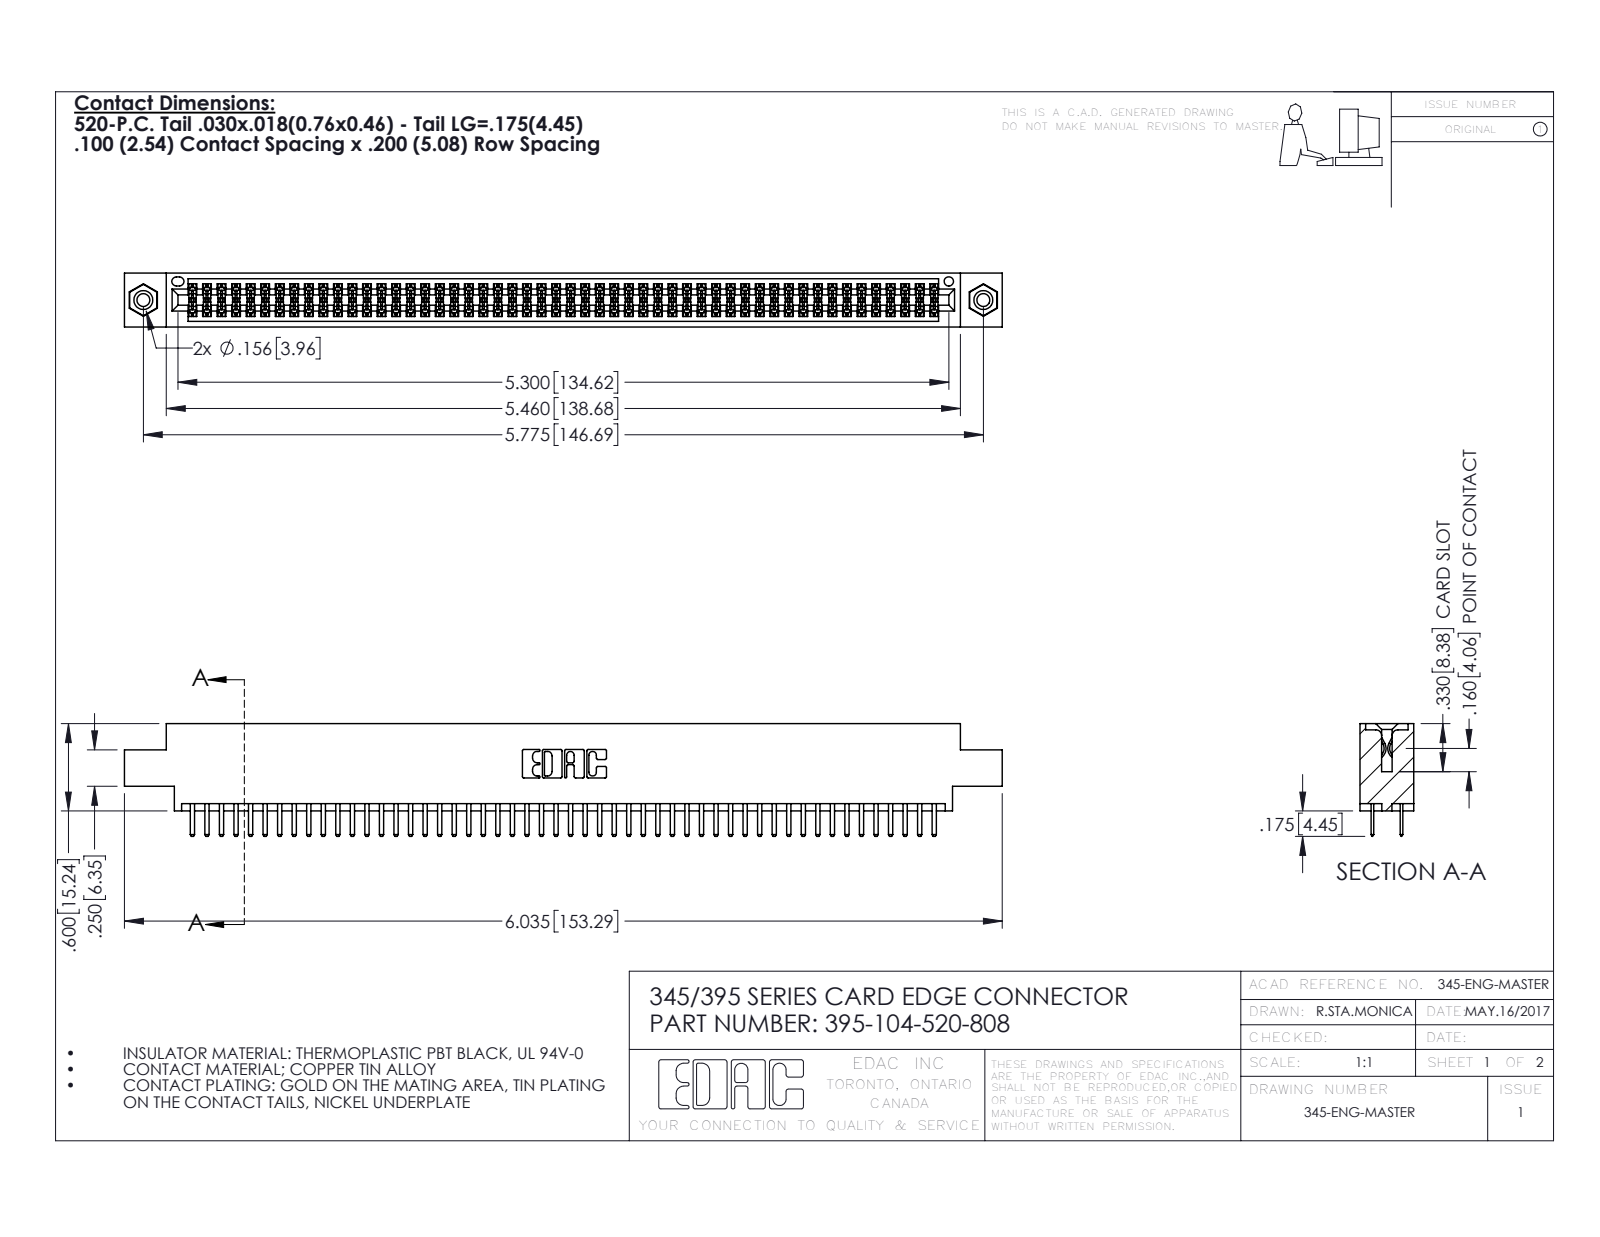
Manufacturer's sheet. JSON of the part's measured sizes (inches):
{"part_name": "395-104-520-808; 345 Part_0.170 Offset - 0.156 Dia-TI; 345-250-001_345-250-003-102; 345-292-001_345-293-120", "step_written_by": "SolidWorks 2016 (CONFIG_CONTROL_DESIGN)", "units": "inches", "bodies": {"solids": 107, "faces": 5806, "planar": 3756, "cylindrical": 2034, "other": 16}, "overall_size": [6.035, 0.775, 0.37], "volume_in3": 0.904, "surface_area_in2": 34.34, "round_holes": [[0.089, 2], [0.125, 2], [0.156, 2], [0.064, 1]], "round_bosses_or_shafts": [[0.155, 2]], "partial_cylinders_radius": [[0.006, 156], [0.01, 108], [0.01, 22], [0.007, 6], [0.031, 6], [0.026, 3], [0.014, 2], [0.019, 2]], "face_to_face_distances": [0.072, 0.298, 0.2, 0.37, 0.098, 0.272, 0.025, 0.225, 0.022, 0.072], "hole_center_spacings": [0.27, 5.539, 5.775]}
